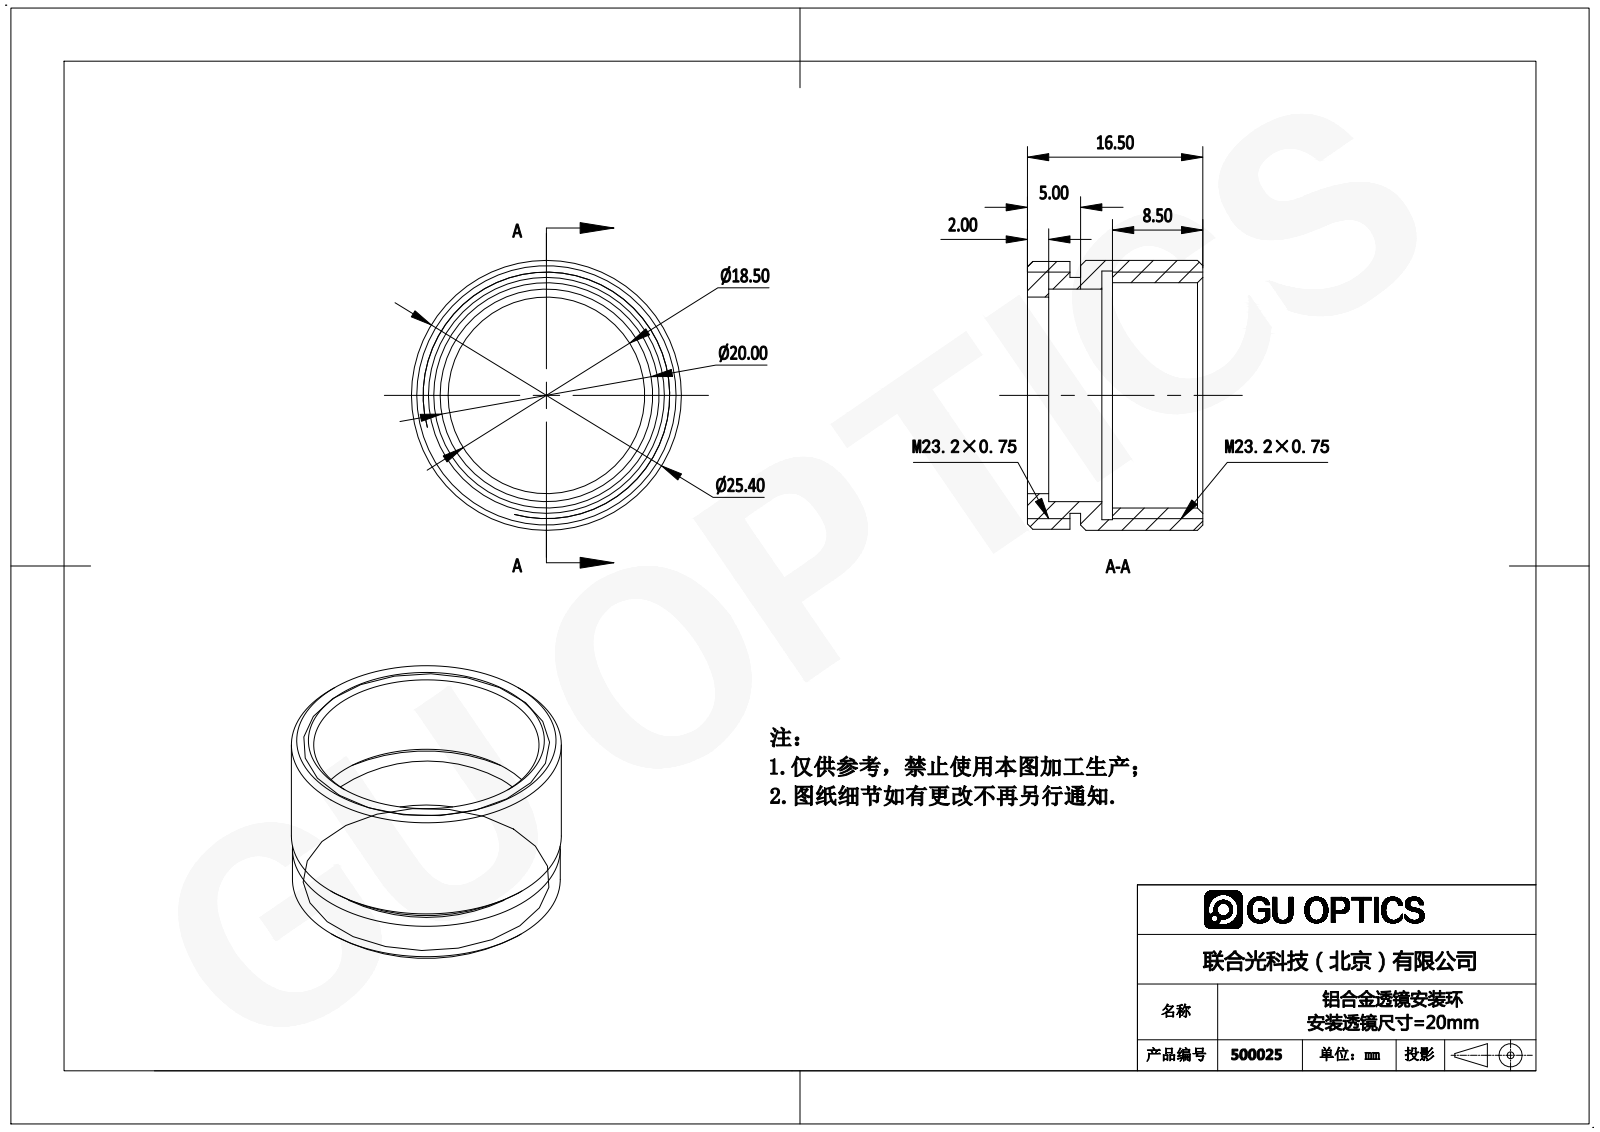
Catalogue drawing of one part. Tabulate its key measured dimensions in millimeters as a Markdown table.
| quantity | value |
| --- | --- |
| part name | 500025 |
| STEP written by | SolidWorks 2016 (AUTOMOTIVE_DESIGN) |
| units | millimeters |
| bodies | 1 solid, 29 faces (7 planar, 14 cylindrical, 8 other) |
| overall size | 25.4 × 25.4 × 16.5 |
| volume | 2 632 mm³ |
| surface area | 3 137 mm² |
| round holes (diameter × count) | 18.5 × 1, 20 × 1, 21.2 × 1, 23.4 × 1 |
| round bosses / shafts (diameter × count) | 25.4 × 1, 25.2 × 1, 22.2 × 1 |
| main face-to-face distances | 3, 4, 2, 1, 5, 7, 16.5, 12.5, 11.5, 9.5 |
